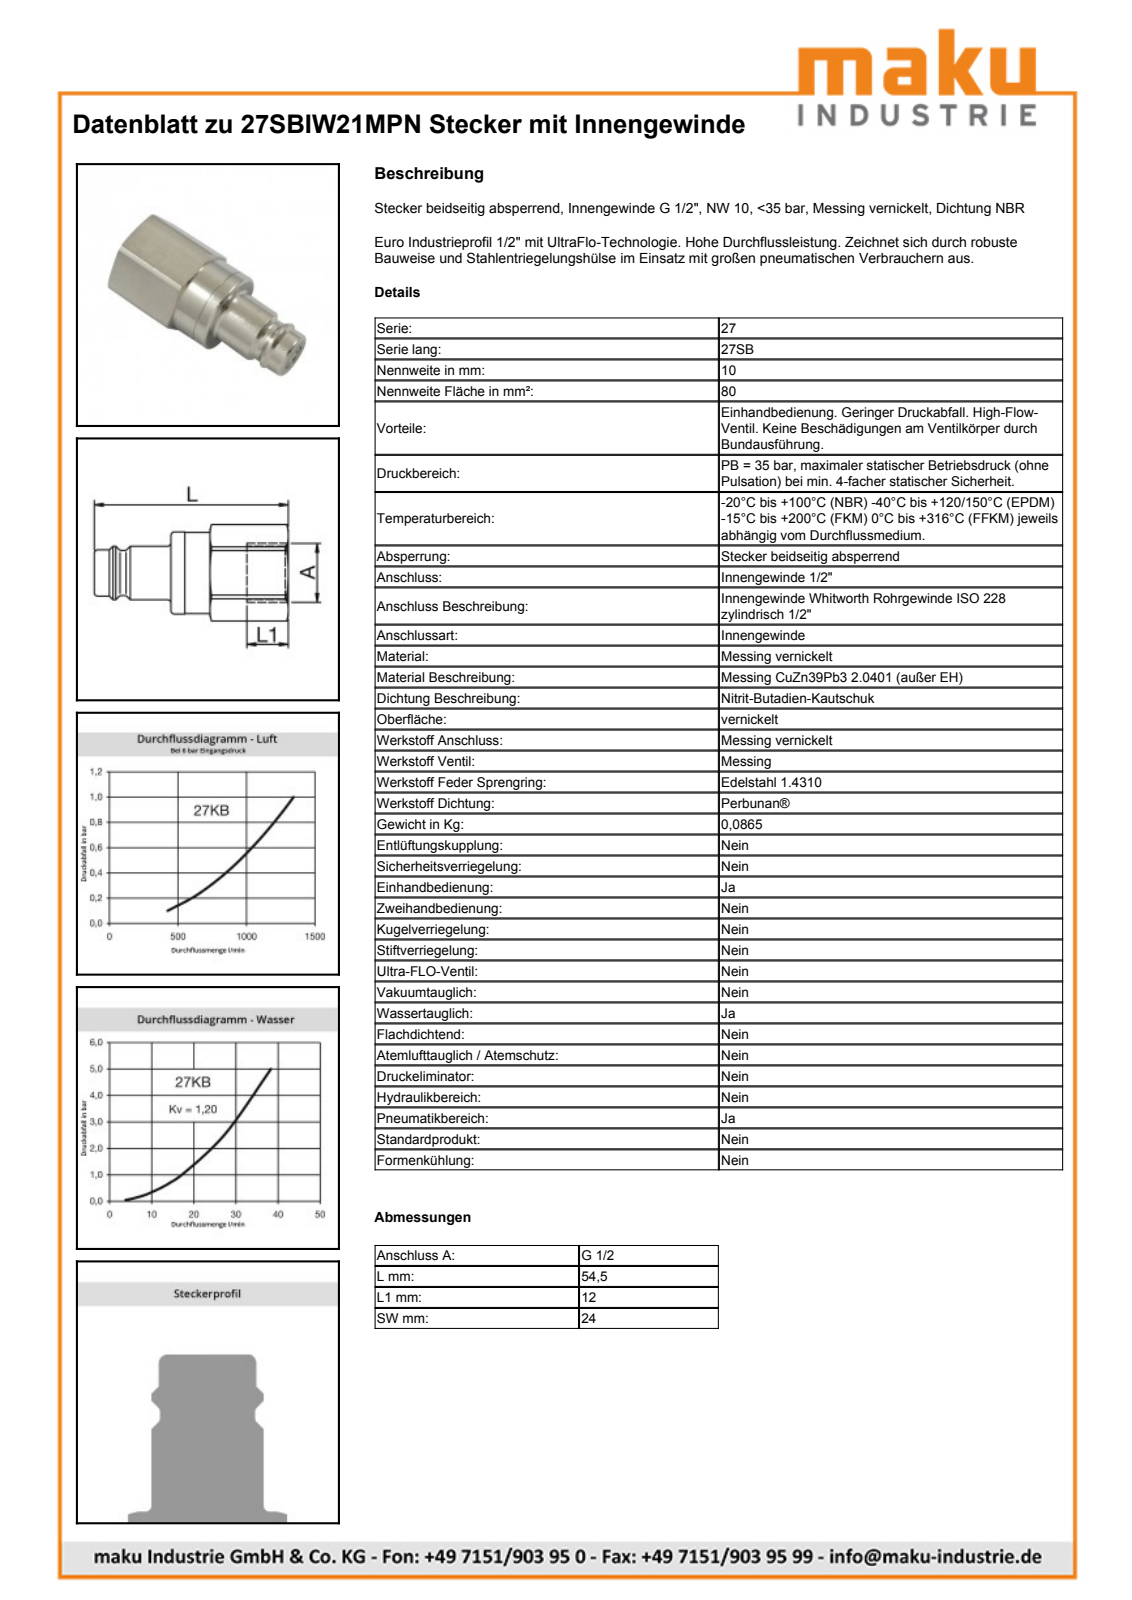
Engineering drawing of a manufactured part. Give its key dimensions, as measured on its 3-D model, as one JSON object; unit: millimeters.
{"part_name": "D106731", "step_written_by": "Autodesk Inventor 2013 (AUTOMOTIVE_DESIGN)", "units": "millimeters", "bodies": {"solids": 1, "faces": 81, "planar": 32, "cylindrical": 22, "other": 27}, "overall_size": [54.4, 27.03, 24.98], "volume_mm3": 15488, "surface_area_mm2": 5364, "round_holes": [[18, 1], [18.63, 1], [19, 1]], "round_bosses_or_shafts": [[23, 1], [22.75, 1], [18.5, 1], [15, 1], [13, 1], [12.65, 1]], "partial_cylinders_radius": [[5.58, 1], [13.53, 1]], "face_to_face_distances": [24, 20.89, 32.9, 12.01, 21.5, 42.39, 54.4, 25.4, 3.9, 16.99]}
